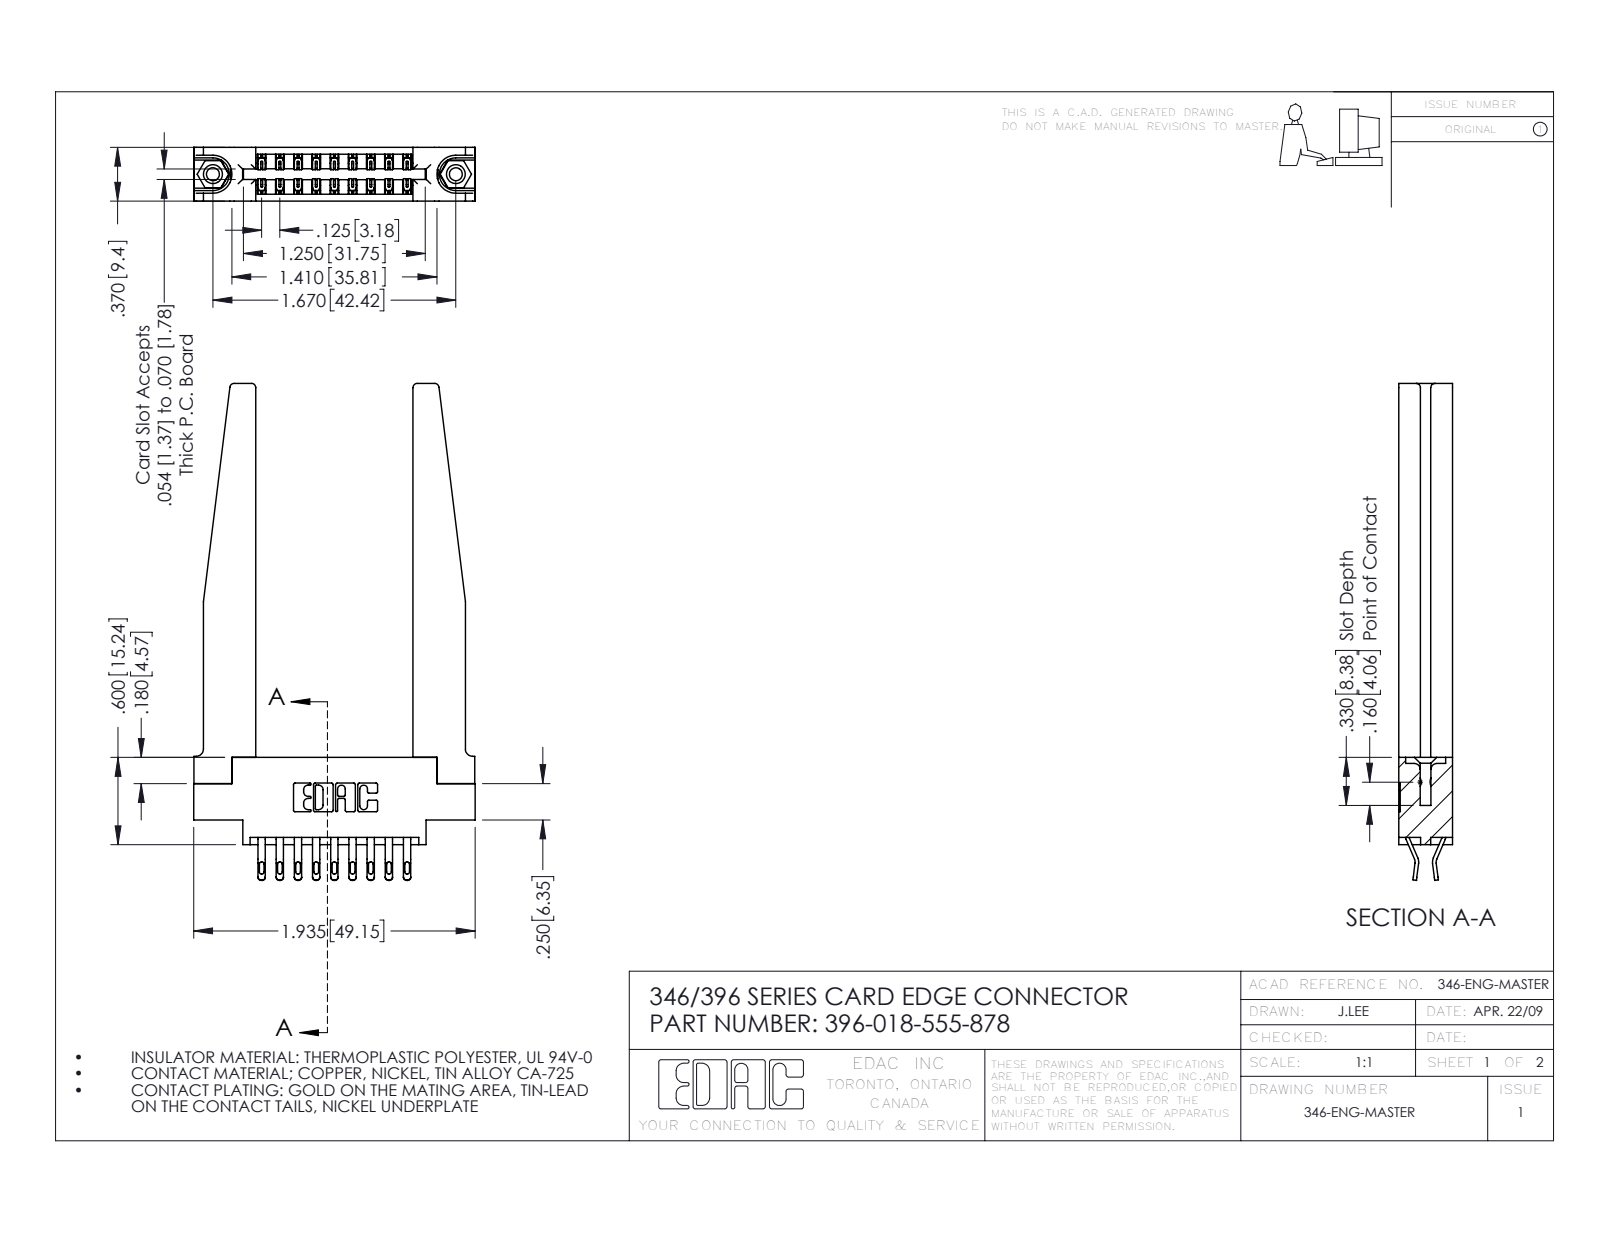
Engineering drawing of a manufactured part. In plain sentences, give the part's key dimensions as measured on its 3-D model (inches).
The part is named "396-018-555-878; 346 Part_0.170 Offset - 0.156 Dia-TH; 345-292-001_555 Tail; 345-250-001_345-250-001-102 (+1 more)". Its 3-D file was written by "SolidWorks 2016 (CONFIG_CONTROL_DESIGN)". It is 23 solids with 1404 faces: 816 planar, 536 cylindrical and 52 other. Overall it measures 3.415 by 1.935 by 0.37 inches. Its volume is 0.692 cubic inches and its surface area 19.34 square inches. Round holes: 2 of diameter 0.089, 2 of diameter 0.125, 2 of diameter 0.156, 1 of diameter 0.064. Round bosses or shafts: 2 of diameter 0.155. Partial cylindrical surfaces (rounded edges, fillets, slot ends): 36 of radius 0.016, 36 of radius 0.02, 27 of radius 0.006, 22 of radius 0.01, 8 of radius 0.03, 6 of radius 0.007, 6 of radius 0.031, 4 of radius 0.05. The main face-to-face distances are 0.37, 0.15, 0.148, 0.072, 0.22, 0.102, 0.048, 0.322, 0.173, 0.25. The hole center spacings are 0.246, 1.465, 1.67.
